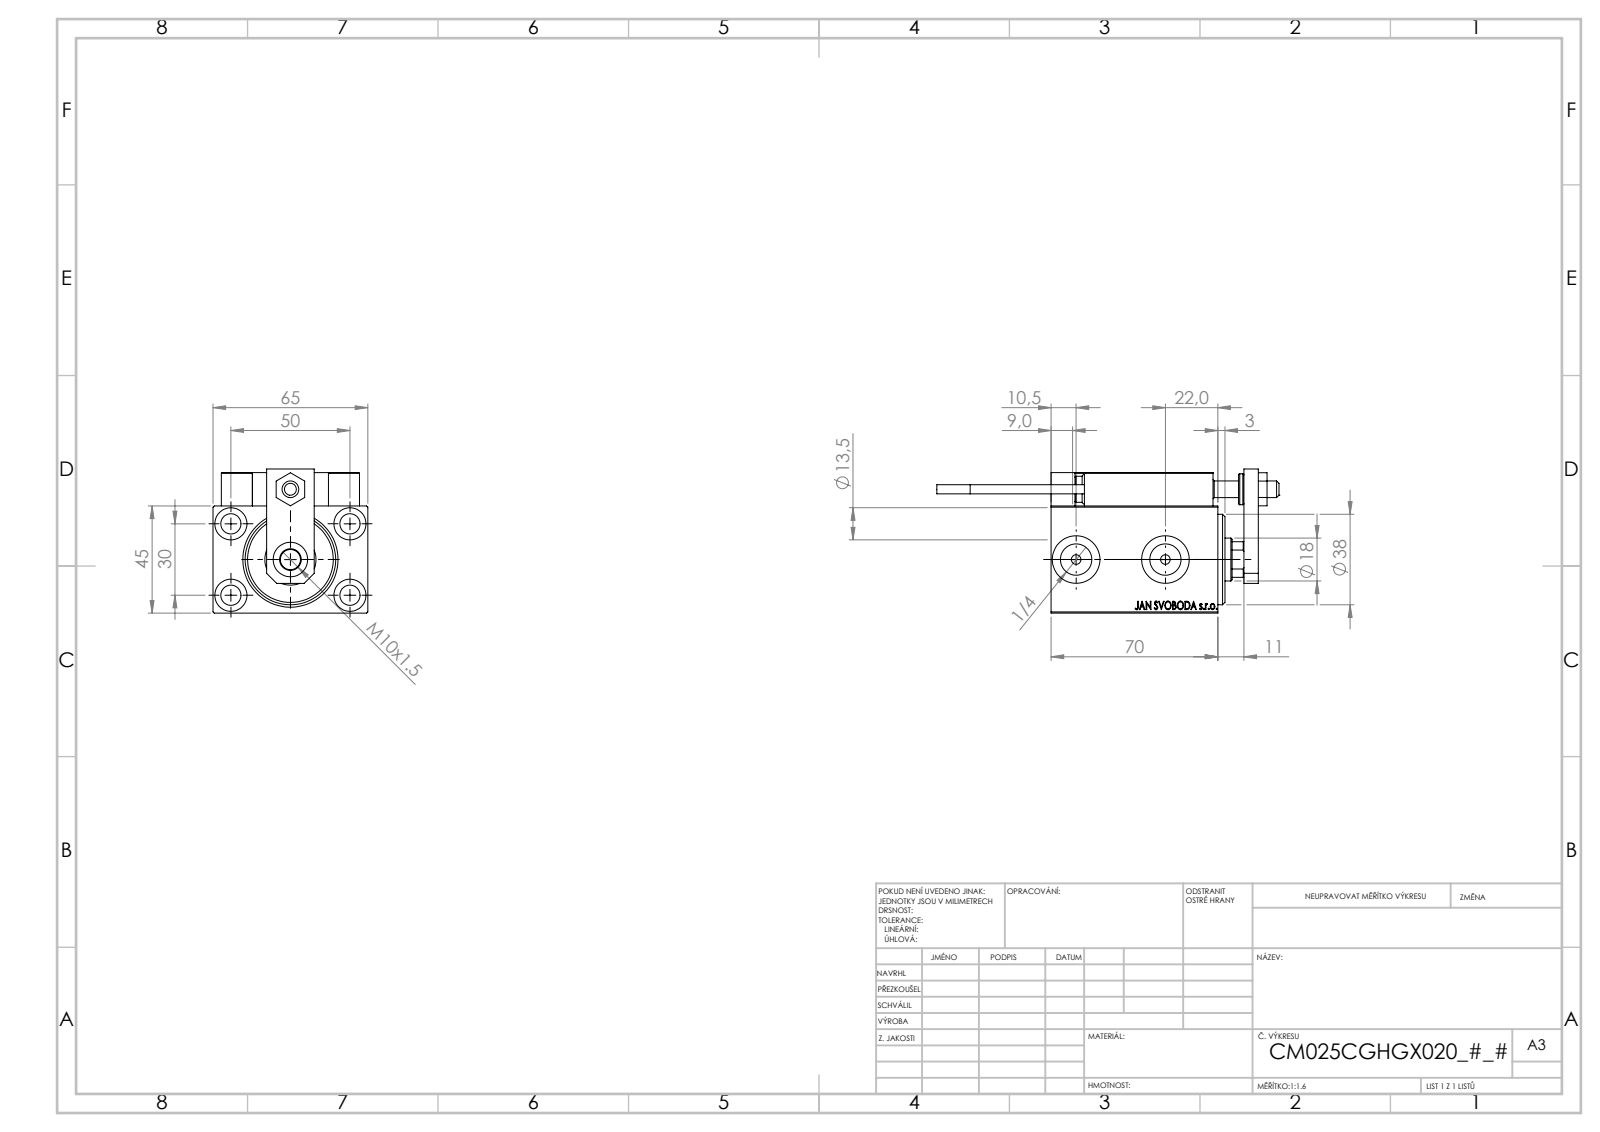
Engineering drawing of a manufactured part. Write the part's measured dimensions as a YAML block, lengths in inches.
part_name: "NUT_D12; ALLEN BOLT D8; V450CM_VC_B; SWITCH_X_FRONT_BACK (+7 more)"
step_written_by: "SolidWorks 2019 (CONFIG_CONTROL_DESIGN)"
units: inches
bodies: {solids: 23, faces: 1282, planar: 560, cylindrical: 188, other: 534}
overall_size: [5.657, 2.559, 2.382]
volume: 13.62
surface_area: 109.7
round_holes:
  - {diameter: 0.157, count: 6}
  - {diameter: 0.315, count: 5}
  - {diameter: 0.335, count: 5}
  - {diameter: 0.126, count: 4}
  - {diameter: 0.531, count: 4}
  - {diameter: 0.197, count: 2}
  - {diameter: 0.518, count: 2}
  - {diameter: 0.787, count: 2}
  - {diameter: 0.276, count: 1}
  - {diameter: 0.571, count: 1}
  - {diameter: 0.709, count: 1}
  - {diameter: 0.846, count: 1}
round_bosses_or_shafts:
  - {diameter: 0.197, count: 2}
  - {diameter: 0.15, count: 2}
  - {diameter: 0.512, count: 1}
  - {diameter: 0.433, count: 1}
partial_cylinders:
  - {radius: 0.012, count: 30}
  - {radius: 0.118, count: 2}
  - {radius: 0.335, count: 1}
face_to_face_distances: [1.772, 2.323, 2.559, 0.551, 0.236, 0.118, 0.276, 0.512, 0.138, 0.197]
hole_center_spacings: [1.148, 0.448, 0.787, 0.87, 1.138, 1.165, 1.169, 1.181]
